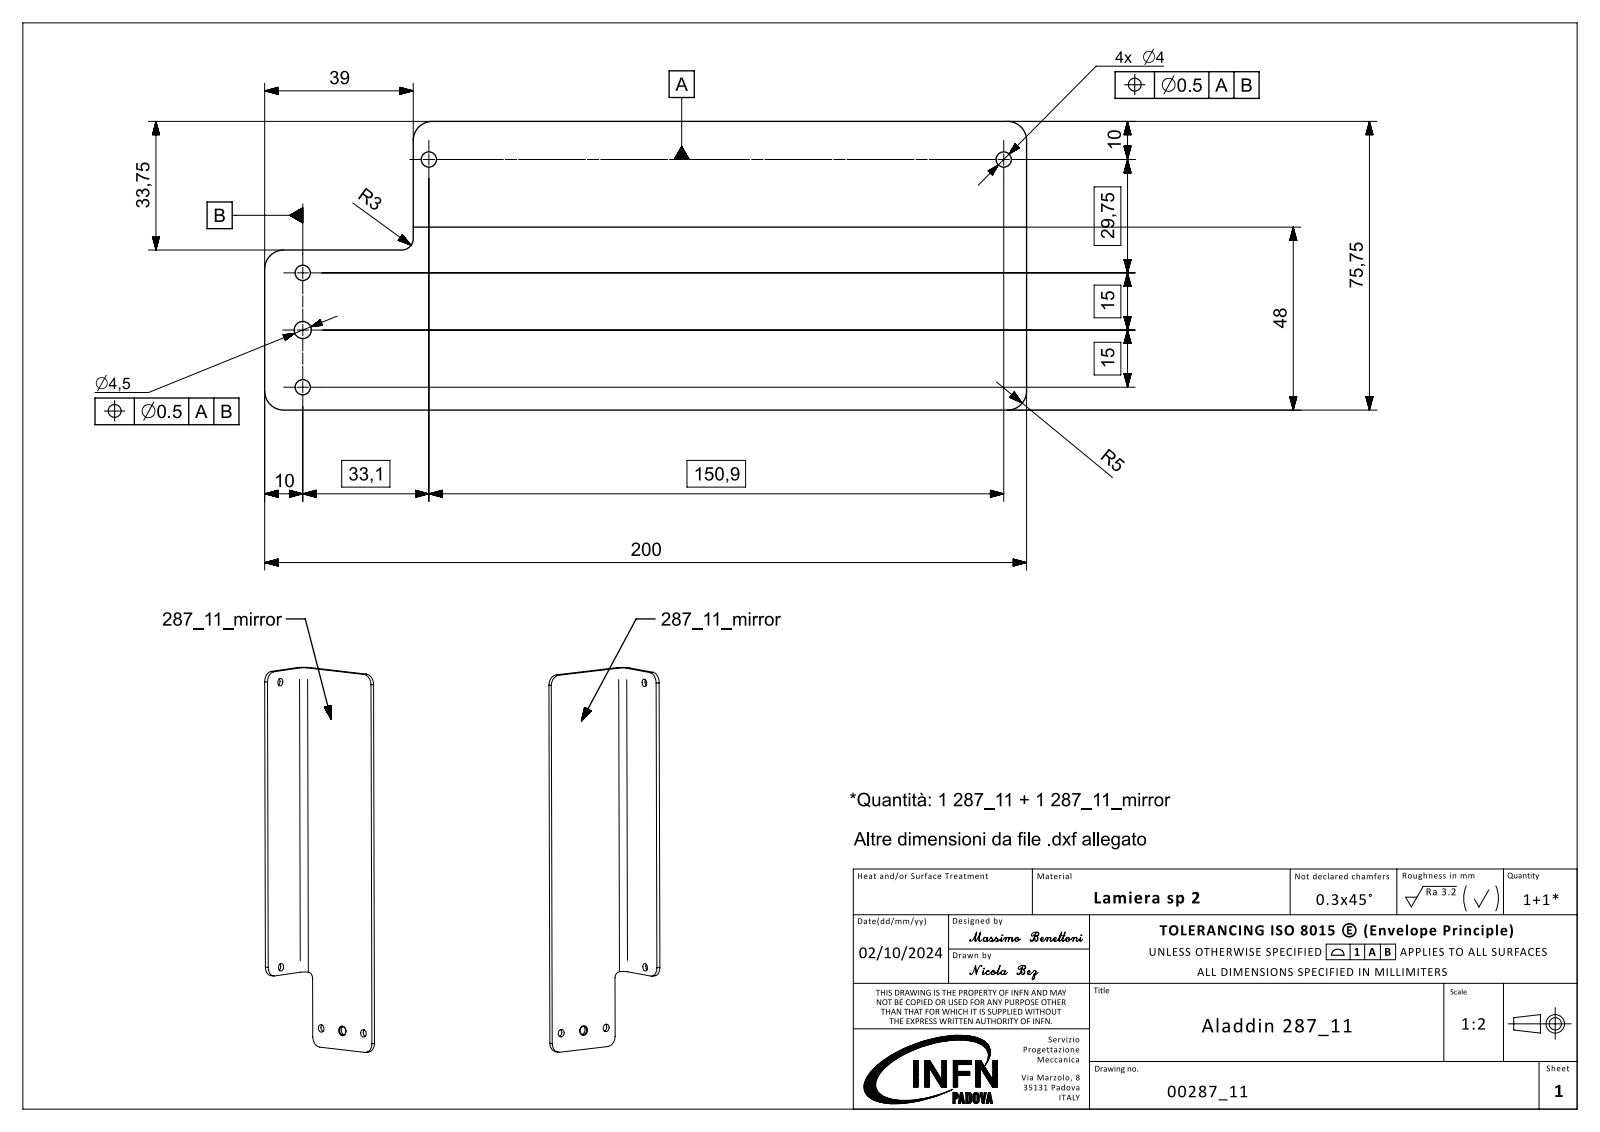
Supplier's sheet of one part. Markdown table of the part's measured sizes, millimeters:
| quantity | value |
| --- | --- |
| part name | 00287_11_objects |
| STEP written by | SIEMENS PLM Software NX2306.9102 (AUTOMOTIVE_DESIGN) |
| units | millimeters |
| bodies | 1 solid, 25 faces (10 planar, 13 cylindrical, 2 other) |
| overall size | 200 × 50 × 30 |
| volume | 27 655 mm³ |
| surface area | 28 861 mm² |
| round holes (diameter × count) | 4 × 4, 4.5 × 1 |
| partial cylindrical surfaces (radius × count) | 5 × 6, 3 × 2 |
| main face-to-face distances | 2, 50, 48, 28, 30, 200, 8, 6, 42, 161 |
| hole center spacings | 15, 30, 150.9 |
